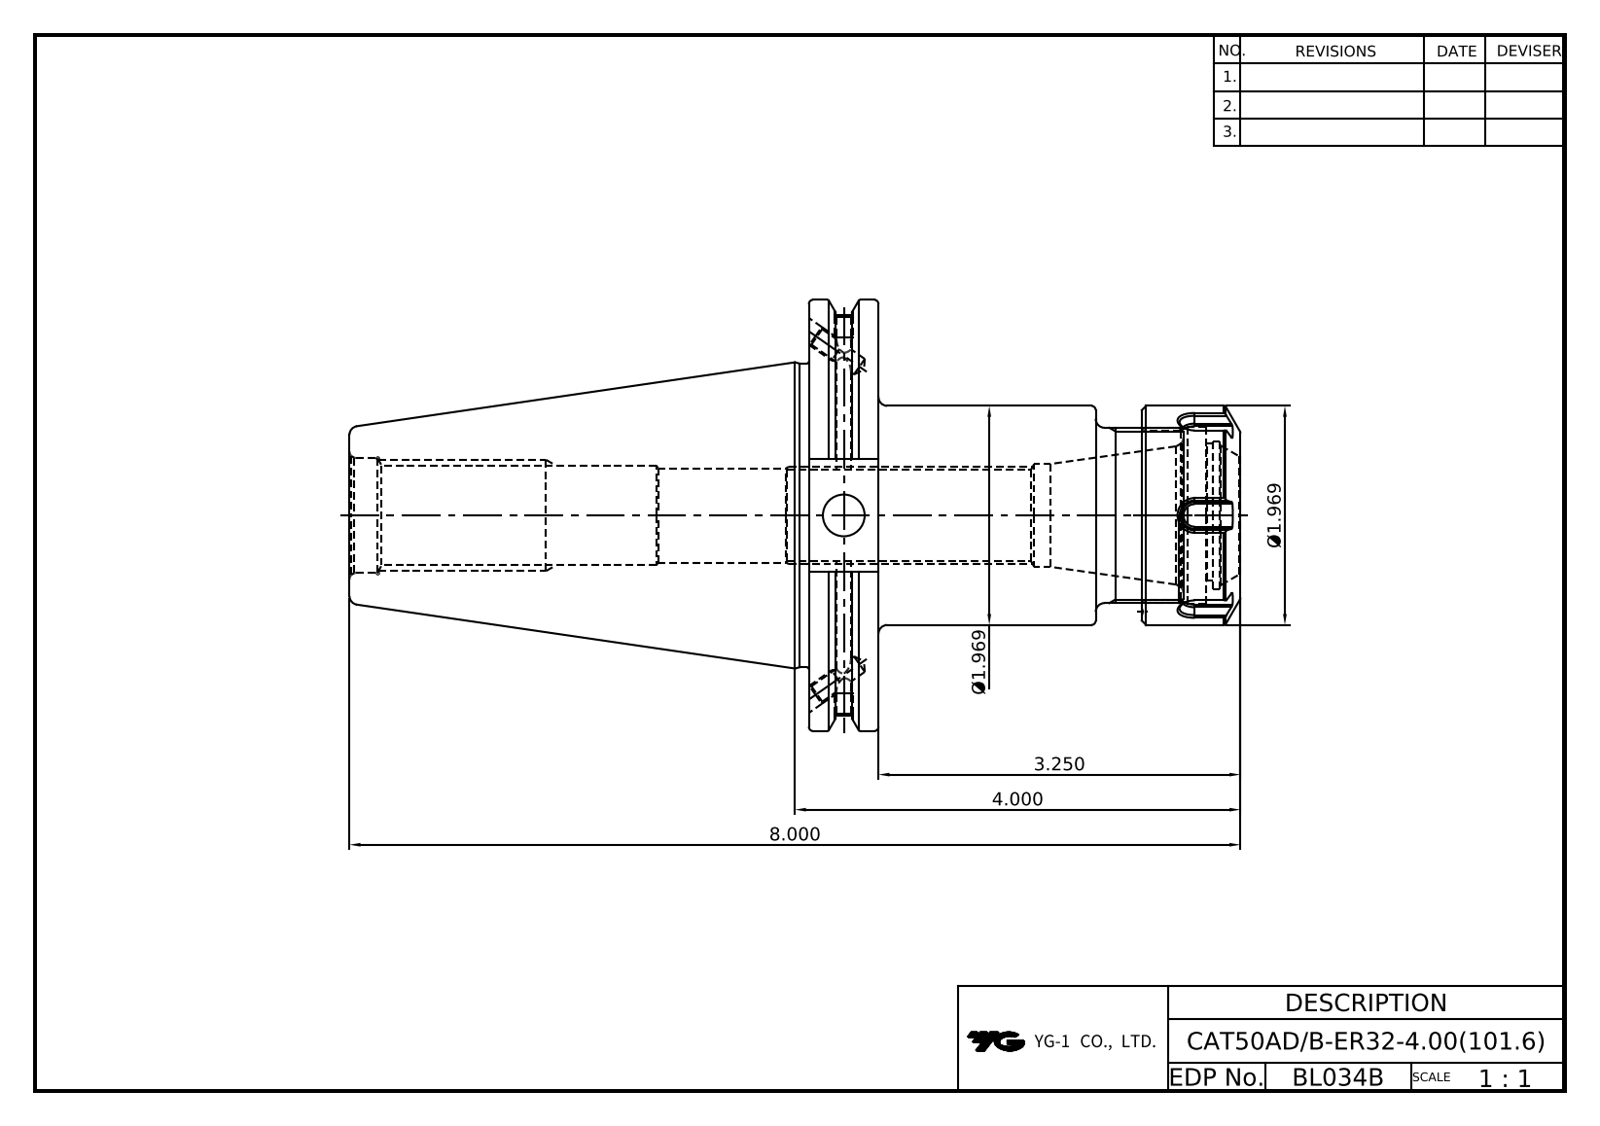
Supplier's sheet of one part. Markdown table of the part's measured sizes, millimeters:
| quantity | value |
| --- | --- |
| part name | LO-CAT50ADB-ER32-4.00; ER32NUT |
| STEP written by | Autodesk Inventor 2024 (AUTOMOTIVE_DESIGN) |
| units | millimeters |
| bodies | 2 solids, 170 faces (72 planar, 45 cylindrical, 53 other) |
| overall size | 203.2 × 98.42 × 94.69 |
| volume | 427 961 mm³ |
| surface area | 68 437 mm² |
| round holes (diameter × count) | 3.24 × 2, 4.13 × 2, 4.2 × 2, 5 × 2, 1 × 1, 9.53 × 1, 20.5 × 1, 21.97 × 1, 23.5 × 1, 26.2 × 1, 27.1 × 1, 31.4 × 1 |
| round bosses / shafts (diameter × count) | 98.42 × 1, 91.29 × 1, 69.25 × 1, 50 × 1, 40 × 1 |
| partial cylindrical surfaces (radius × count) | 0.5 × 12 |
| main face-to-face distances | 15.88, 98.43, 82.55, 75.93, 60.05, 22.5, 104.77, 120.65, 180.7, 203.2 |
| hole center spacings | 0.8, 22, 22.8 |
